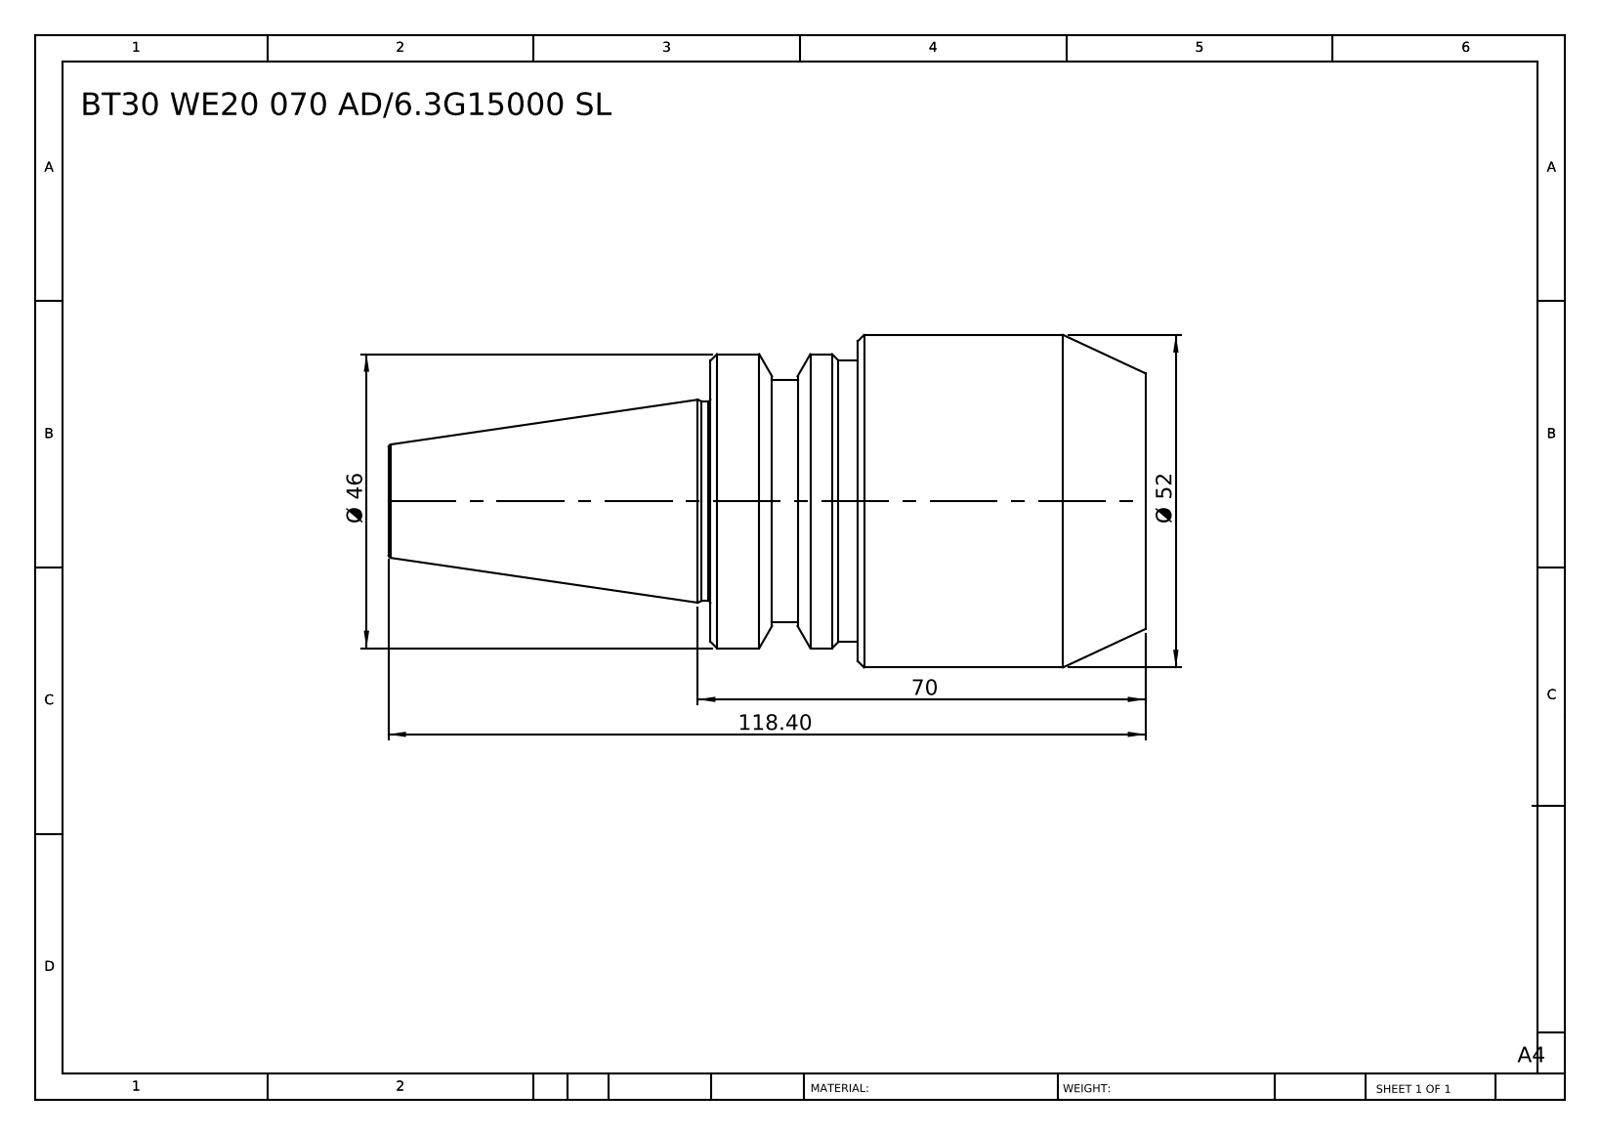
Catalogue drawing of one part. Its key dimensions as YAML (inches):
part_name: "BT30 WE20 070 AD-6.3G15000 SL"
step_written_by: "SolidWorks 2014 (CONFIG_CONTROL_DESIGN)"
units: inches
bodies: {solids: 1, faces: 38, planar: 6, cylindrical: 12, other: 20}
overall_size: [4.661, 2.047, 2.047]
volume: 9.13
surface_area: 27.86
round_bosses_or_shafts:
  - {diameter: 2.047, count: 1}
  - {diameter: 1.811, count: 1}
  - {diameter: 1.732, count: 1}
  - {diameter: 1.496, count: 1}
  - {diameter: 1.228, count: 1}
face_to_face_distances: [2.677, 1.772, 0.906, 4.661, 2.89, 1.984, 2.299, 0.528, 0.378, 2.362]
